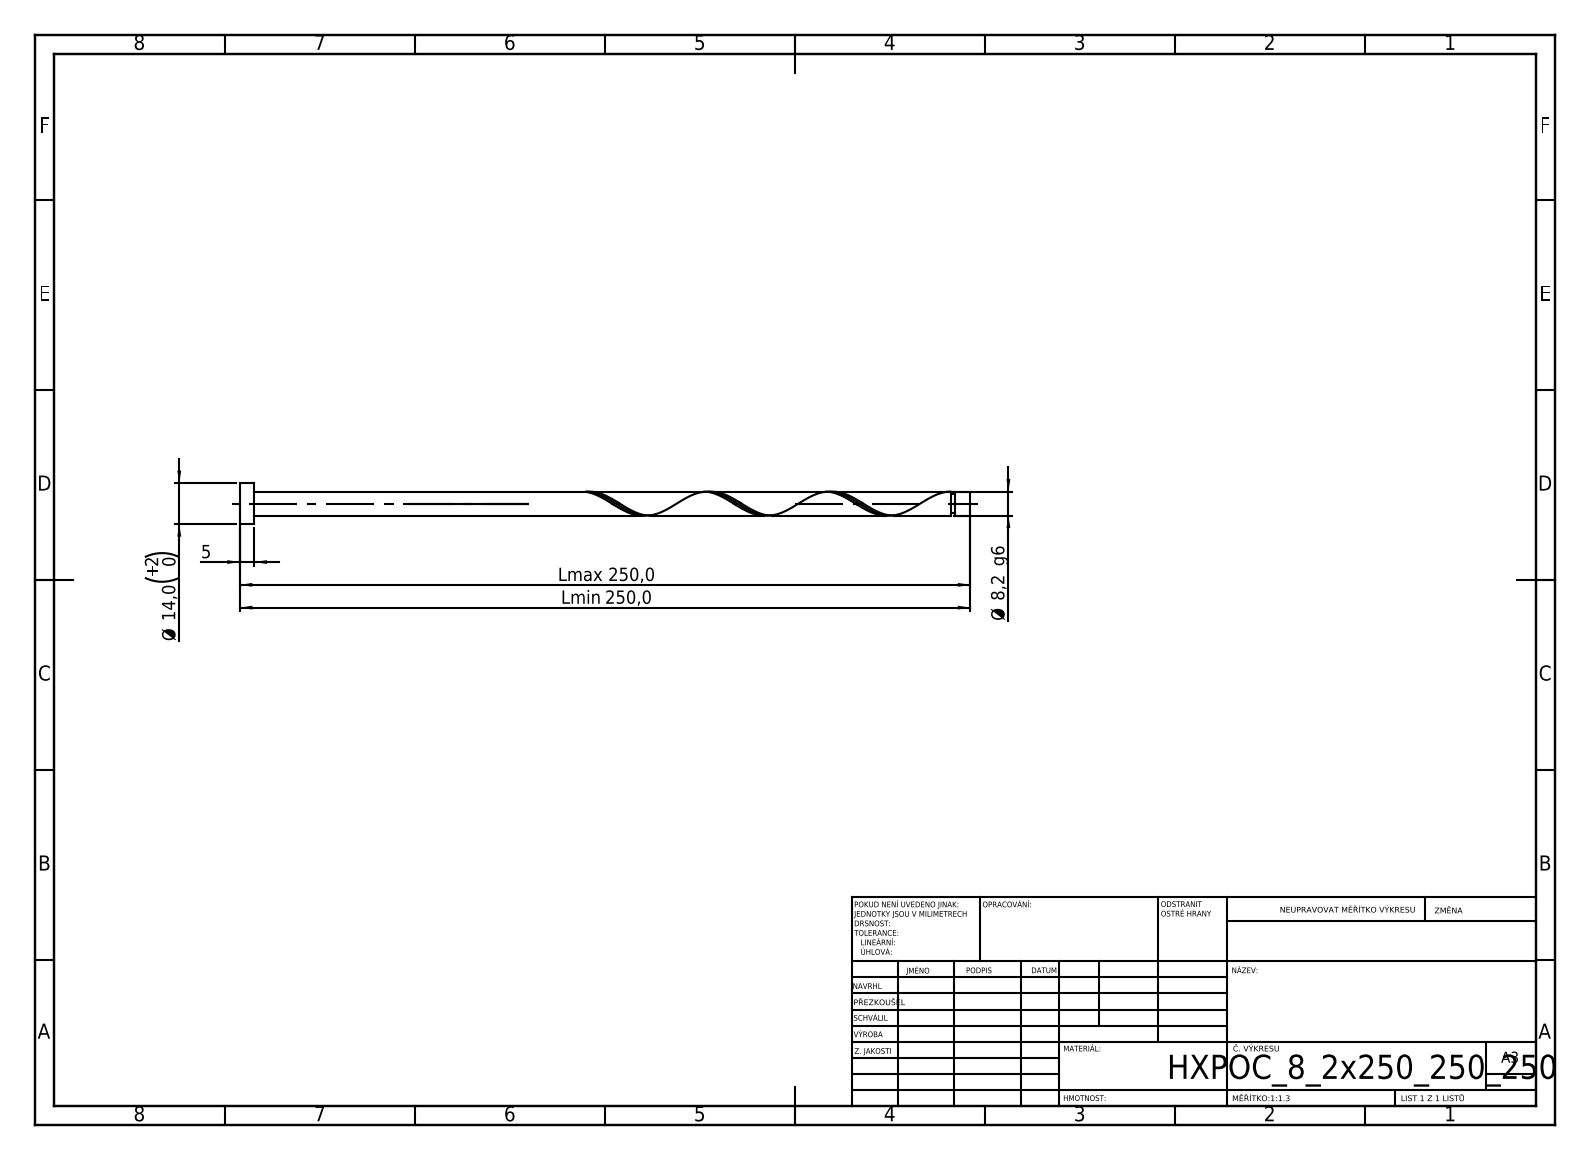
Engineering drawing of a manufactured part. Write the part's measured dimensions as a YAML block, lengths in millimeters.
step_written_by: "SolidWorks 2019 (CONFIG_CONTROL_DESIGN)"
units: millimeters
bodies: {solids: 1, faces: 21, planar: 6, cylindrical: 14, other: 1}
overall_size: [250, 14, 14]
volume: 13551
surface_area: 6990
round_bosses_or_shafts:
  - {diameter: 14, count: 1}
  - {diameter: 8.2, count: 1}
  - {diameter: 6.56, count: 1}
face_to_face_distances: [5, 250, 245, 244.89, 239.89, 5.11, 243.25, 238.25, 1.64, 6.75]
